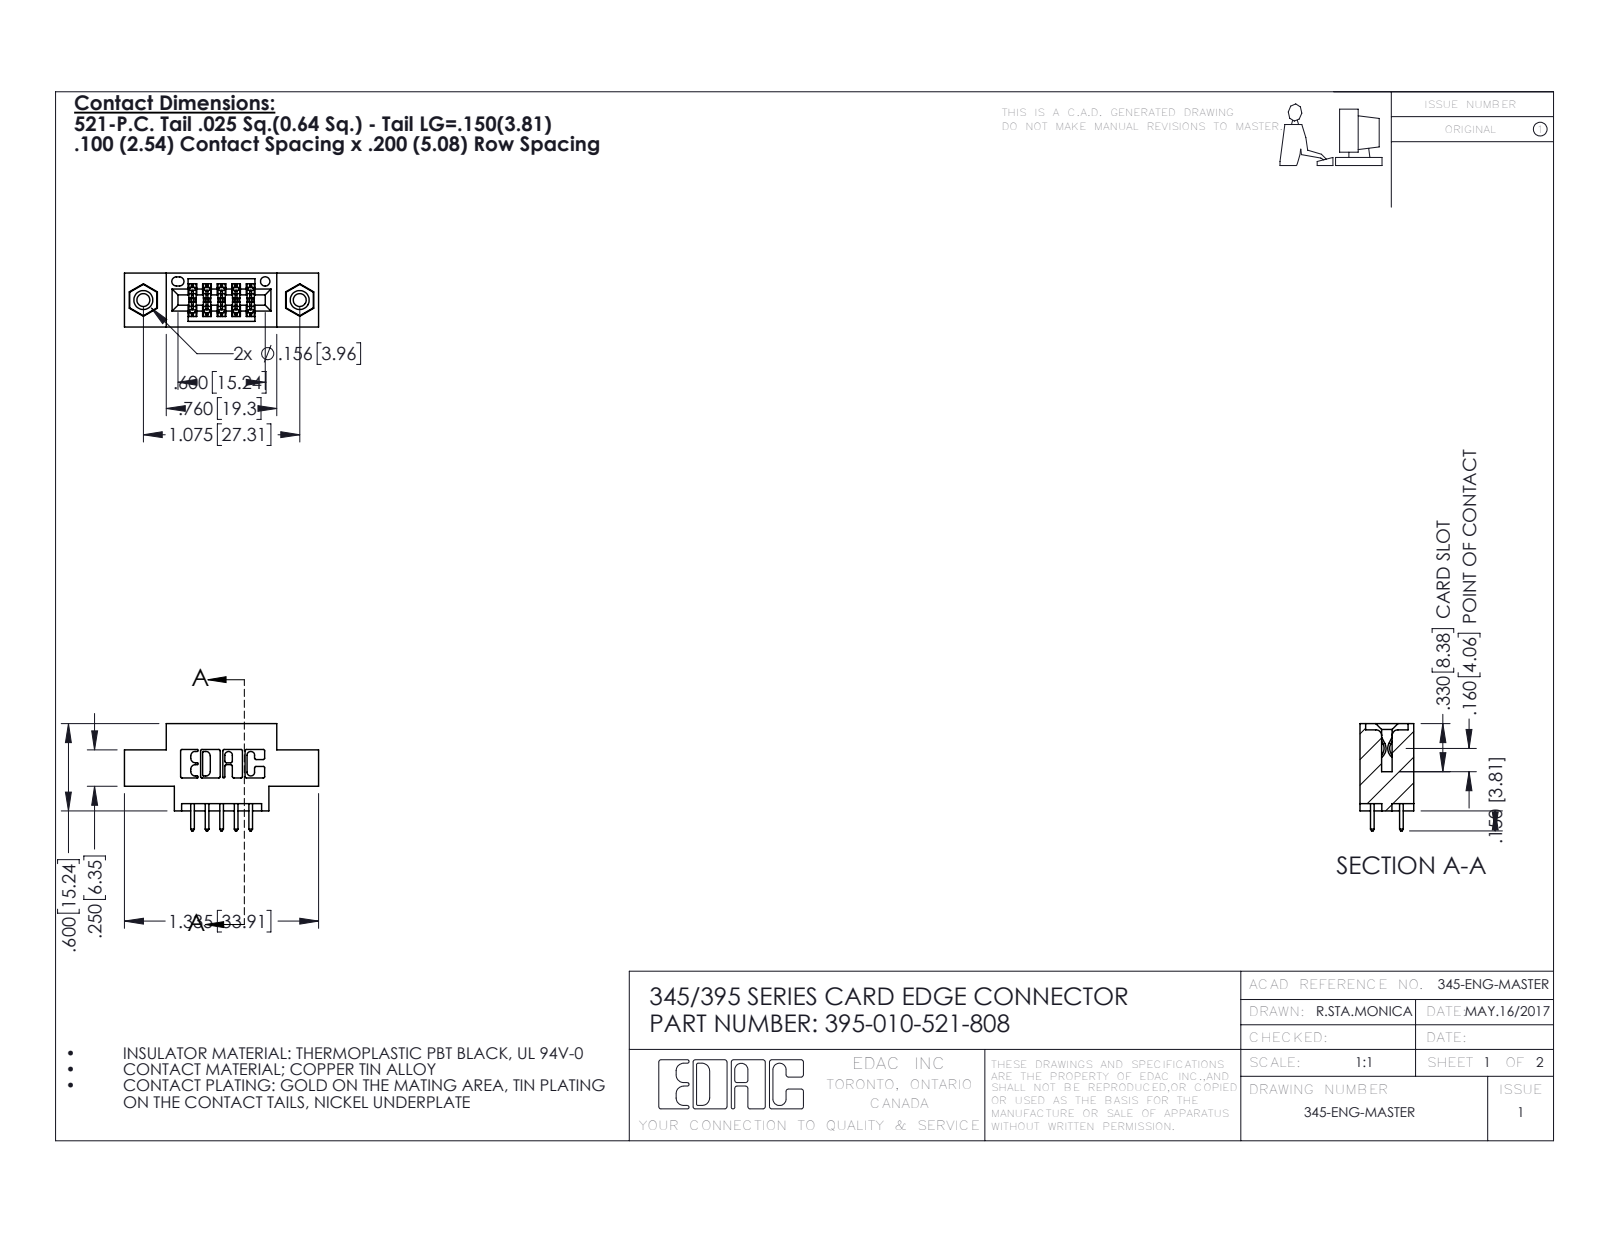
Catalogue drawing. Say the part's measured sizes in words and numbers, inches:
The part is named "395-010-521-808; 345 Part_0.170 Offset - 0.156 Dia-TI; 345-292-001_345-293-121; 345-250-001_345-250-003-102". Its 3-D file was written by "SolidWorks 2016 (CONFIG_CONTROL_DESIGN)". It is 13 solids with 690 faces: 446 planar, 228 cylindrical and 16 other. Overall it measures 1.335 by 0.737 by 0.37 inches. Its volume is 0.172 cubic inches and its surface area 5.567 square inches. Round holes: 2 of diameter 0.089, 2 of diameter 0.125, 2 of diameter 0.156, 1 of diameter 0.064. Round bosses or shafts: 2 of diameter 0.155. Partial cylindrical surfaces (rounded edges, fillets, slot ends): 22 of radius 0.01, 15 of radius 0.006, 10 of radius 0.01, 6 of radius 0.007, 6 of radius 0.031, 3 of radius 0.026, 2 of radius 0.014, 2 of radius 0.019. The main face-to-face distances are 0.37, 0.2, 0.072, 0.298, 0.1, 0.025, 0.098, 0.272, 0.25, 0.225. The hole center spacings are 0.27, 0.847, 1.075.
